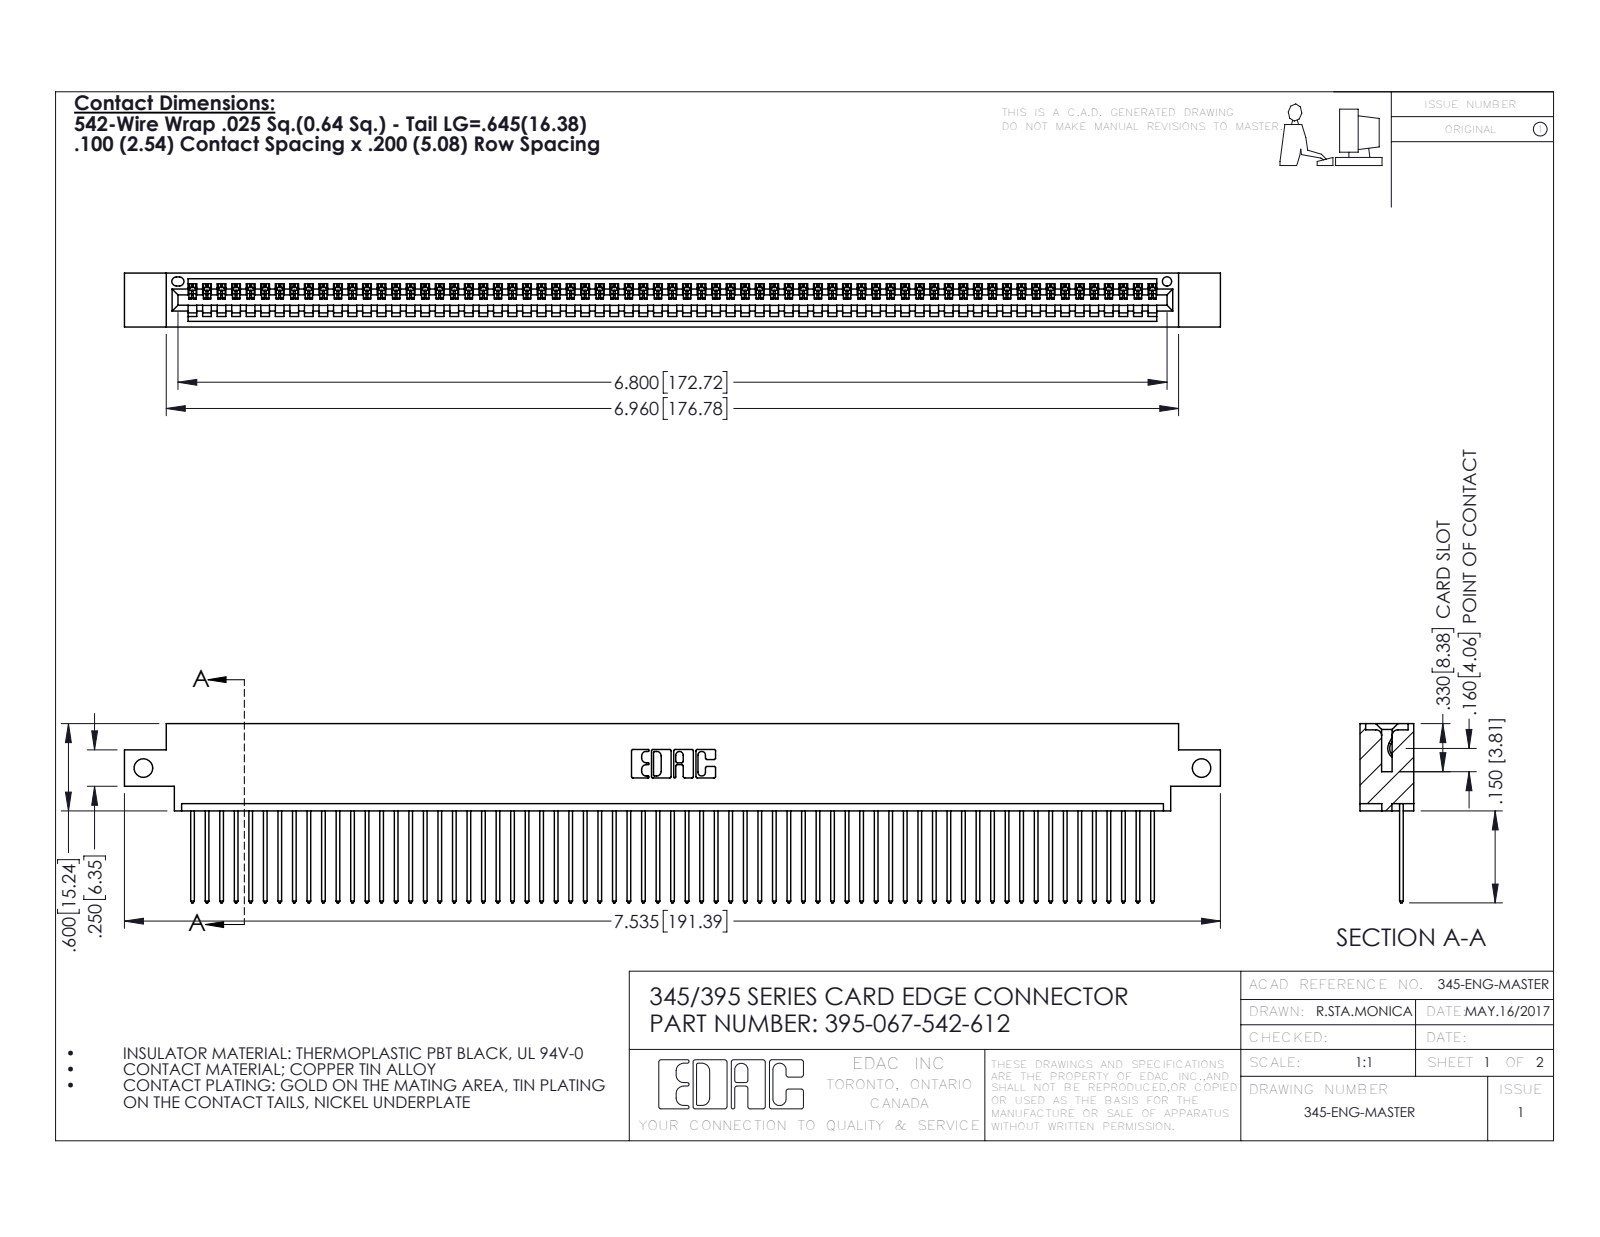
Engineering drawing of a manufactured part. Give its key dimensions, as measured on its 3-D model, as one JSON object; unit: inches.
{"part_name": "345-292-001_345-293-142; 395-067-542-612; 345 Part_0.170 Offset - Side Mount", "step_written_by": "SolidWorks 2016 (CONFIG_CONTROL_DESIGN)", "units": "inches", "bodies": {"solids": 68, "faces": 4016, "planar": 2764, "cylindrical": 1252, "other": 0}, "overall_size": [7.535, 1.232, 0.37], "volume_in3": 1.119, "surface_area_in2": 39.72, "round_holes": [[0.128, 2], [0.064, 1]], "partial_cylinders_radius": [[0.006, 134], [0.01, 134], [0.01, 22], [0.007, 6], [0.031, 6], [0.026, 3], [0.031, 2], [0.04, 2]], "face_to_face_distances": [0.072, 0.298, 0.37, 0.098, 0.272, 0.025, 0.2, 0.225, 0.175, 0.149], "hole_center_spacings": [7.275]}
